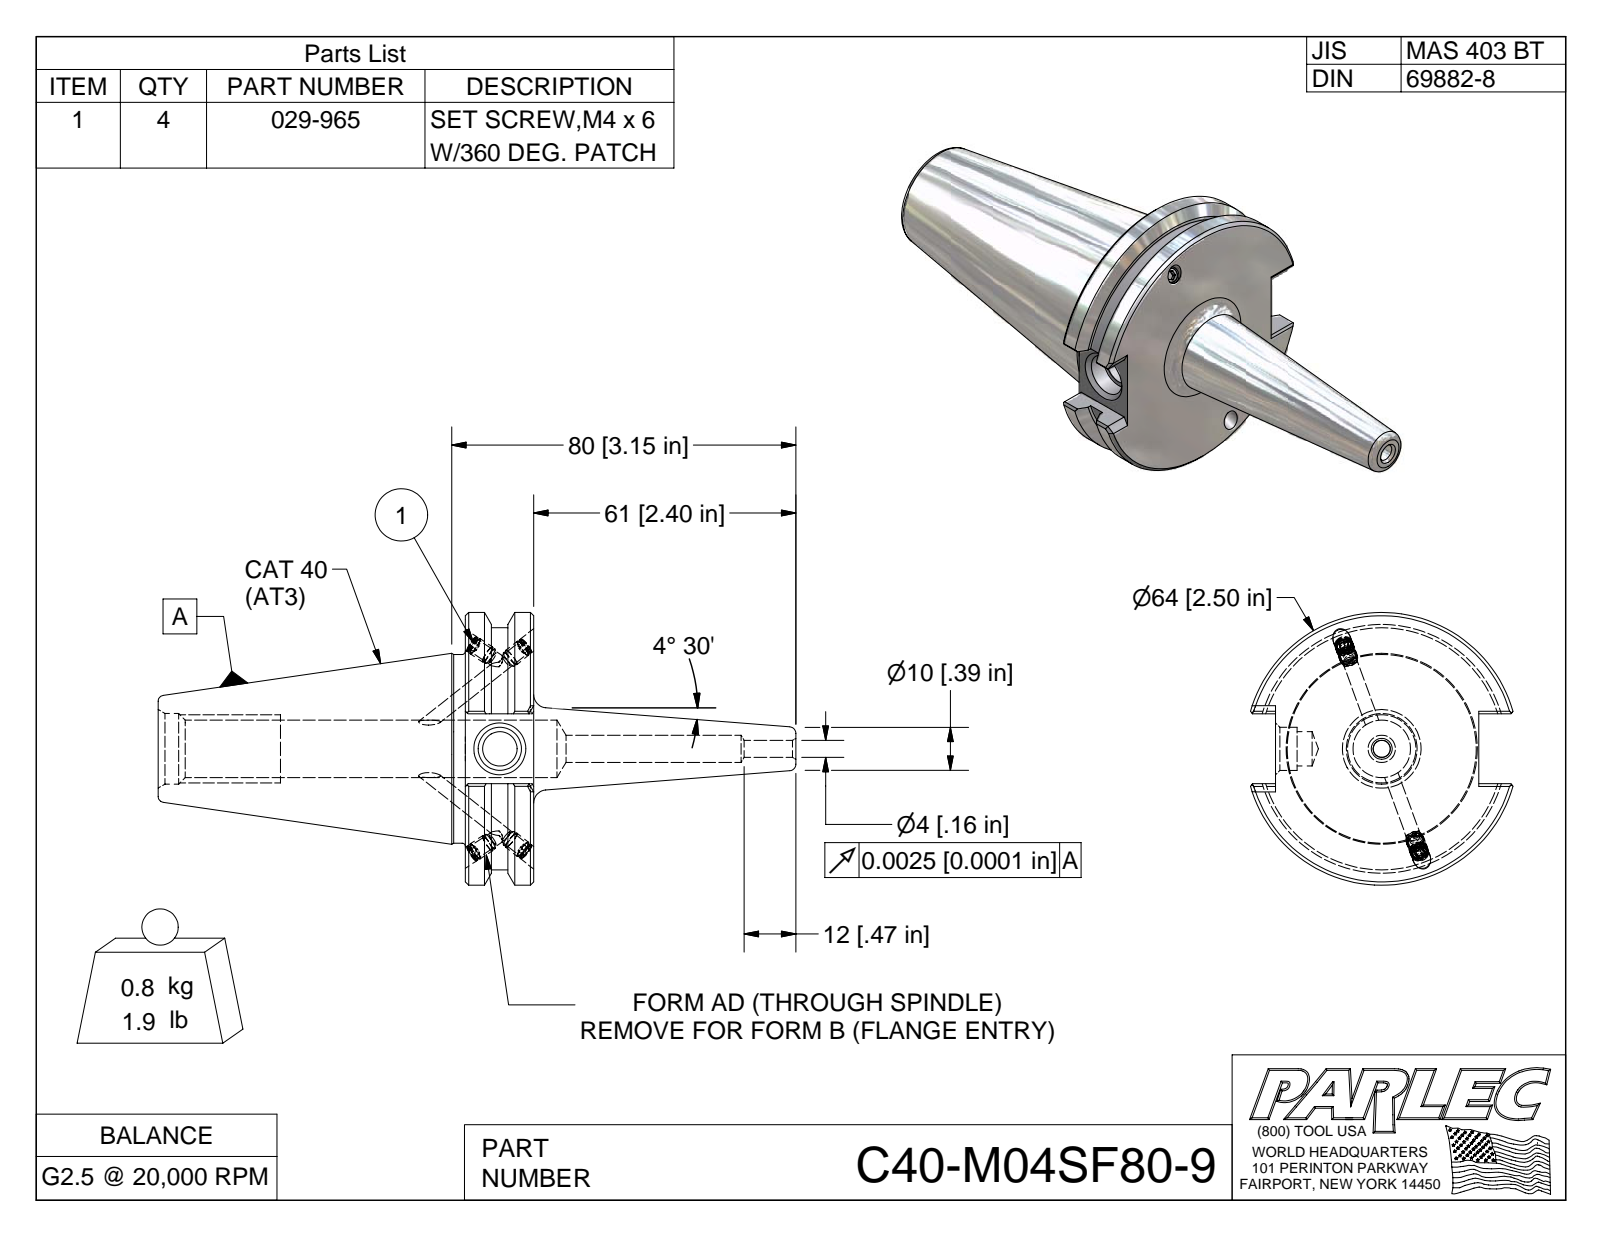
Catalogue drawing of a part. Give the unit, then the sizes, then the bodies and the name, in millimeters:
Units: millimetres
Overall size (bounding box): 148.3 × 63.5 × 61
Round holes (diameter × count): ⌀3.3 ×4, ⌀4.1 ×4, ⌀4 ×1
Round bosses / shafts (diameter × count): ⌀4.2 ×4, ⌀4 ×4, ⌀63.5 ×1, ⌀56.4 ×1, ⌀43.9 ×1
Main face-to-face distances: 15.9, 16.3, 47.2, 71.4, 87.3, 81.3, 9.9, 6, 77.5, 6
Volume: 108 400 mm³ · Surface area: 25 410 mm²
Bodies: 5 solids, 149 faces (76 planar, 28 cylindrical, 45 other)
Part name (STEP PRODUCT): C40-M04SF80-9; C40BC-M04SF80-9-1; 029-965
STEP written by: Autodesk Inventor 2009 (AUTOMOTIVE_DESIGN)
